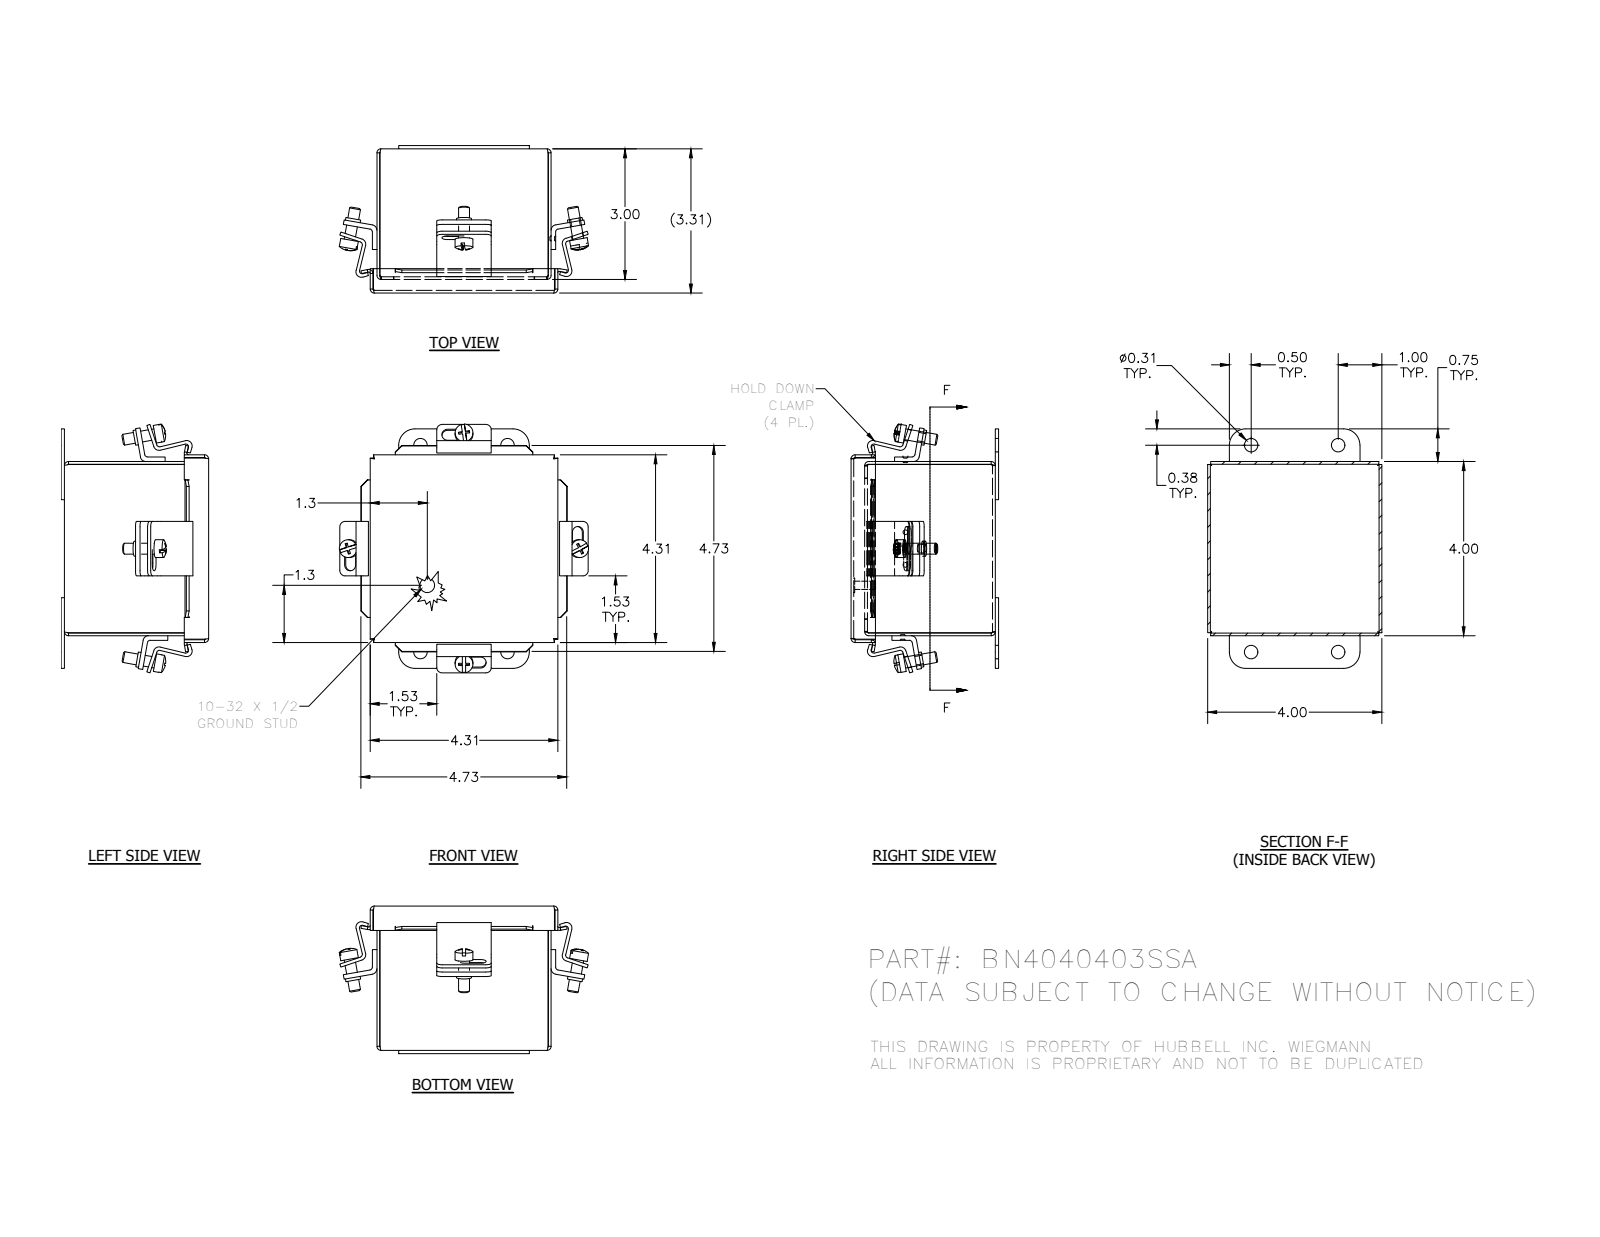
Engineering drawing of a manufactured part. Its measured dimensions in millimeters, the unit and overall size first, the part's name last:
Units: millimetres
Overall size (bounding box): 145.4 × 145.1 × 86.1
Round holes (diameter × count): ⌀2.8 ×6, ⌀5 ×4, ⌀7.9 ×4
Round bosses / shafts (diameter × count): ⌀10.4 ×4, ⌀8.7 ×4, ⌀6.4 ×4, ⌀8.6 ×1, ⌀4.8 ×1
Partial cylindrical surfaces — rounded edges, fillets, slot ends (radius × count): R0.8 ×16, R2.4 ×16, R3.2 ×16, R1.6 ×12, R3.2 ×12, R3.4 ×8, R9.5 ×4
Main face-to-face distances: 1.6, 100, 82.6, 101.6, 98.4, 84.2, 80.9, 1.9, 3.9, 104
Hole centre spacings: 19.1, 1.6, 19.1, 50.8, 120.7, 130.9
Volume: 130 900 mm³ · Surface area: 159 700 mm²
Bodies: 17 solids, 529 faces (275 planar, 176 cylindrical, 78 other)
Part name (STEP PRODUCT): 348127_1; BN4040403SSABKP_1; 372164_1; 30811_1 (+4 more)
STEP written by: SolidWorks 2014 (AUTOMOTIVE_DESIGN)
